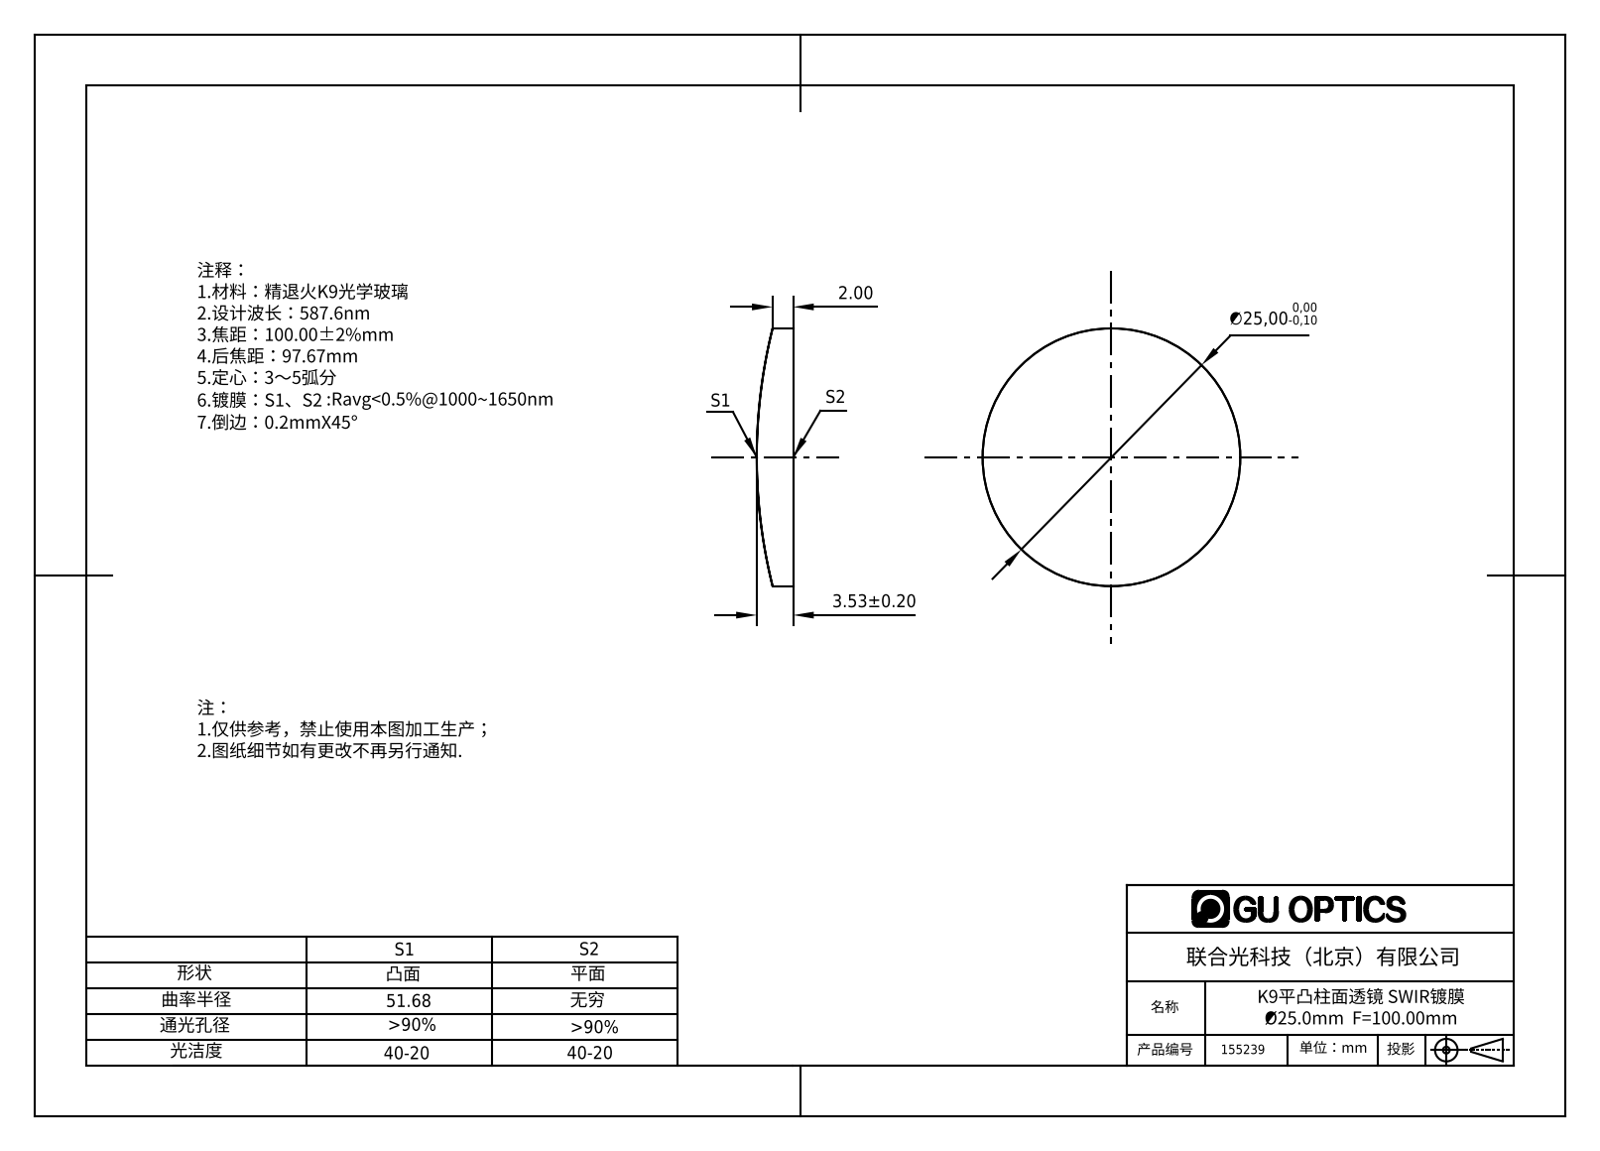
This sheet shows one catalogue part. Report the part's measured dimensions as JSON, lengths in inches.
{"part_name": "155041", "step_written_by": "SolidWorks 2016 (AUTOMOTIVE_DESIGN)", "units": "inches", "bodies": {"solids": 1, "faces": 4, "planar": 1, "cylindrical": 3, "other": 0}, "overall_size": [0.984, 0.984, 0.139], "volume_in3": 0.094, "surface_area_in2": 1.865, "round_bosses_or_shafts": [[0.984, 1]], "partial_cylinders_radius": [[2.035, 1]]}
